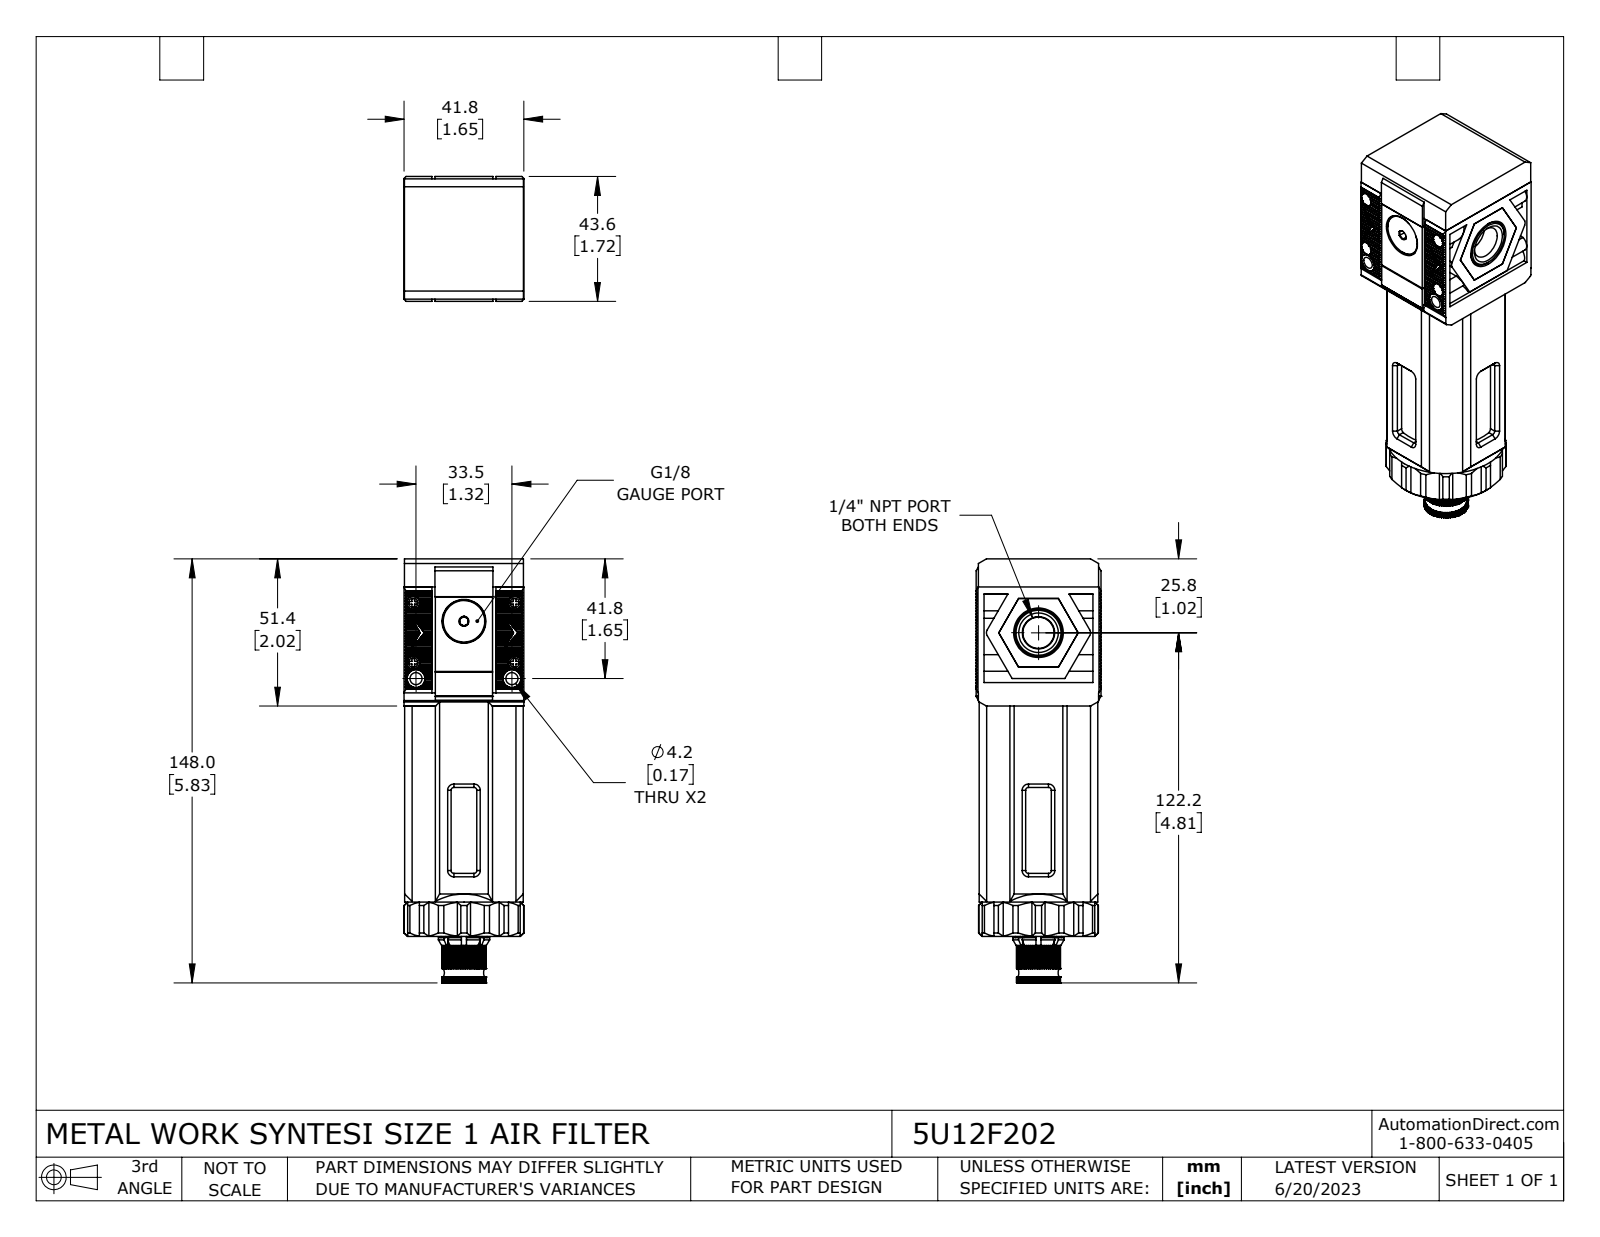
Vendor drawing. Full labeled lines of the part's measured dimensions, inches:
Part name (STEP PRODUCT): 5U12F202
STEP written by: SolidWorks 2021 (CONFIG_CONTROL_DESIGN)
Units: inches
Bodies: 14 solids, 1872 faces (1424 planar, 286 cylindrical, 162 other)
Overall size (bounding box): 5.827 × 1.717 × 1.646
Volume: 7.983 in³ · Surface area: 101.3 in²
Round holes (diameter × count): ⌀0.083 ×4, ⌀0.118 ×4, ⌀0.185 ×4, ⌀0.165 ×2, ⌀0.126 ×1, ⌀0.276 ×1, ⌀0.337 ×1, ⌀0.343 ×1, ⌀0.602 ×1, ⌀1.181 ×1, ⌀1.339 ×1, ⌀1.394 ×1
Round bosses / shafts (diameter × count): ⌀0.181 ×4, ⌀0.102 ×4, ⌀0.244 ×2, ⌀1.63 ×1, ⌀1.402 ×1, ⌀0.984 ×1, ⌀0.898 ×1, ⌀0.717 ×1
Partial cylindrical surfaces — rounded edges, fillets, slot ends (radius × count): R0.039 ×8, R0.024 ×4, R0.122 ×4, R0.008 ×2, R0.079 ×2, R0.276 ×1, R0.28 ×1, R0.354 ×1
Main face-to-face distances: 1.638, 1.63, 0.043, 1.673, 0.386, 1.331, 1.642, 0.307, 1.575, 0.067
Hole centre spacings: 0.222, 0.742, 0.823, 0.9, 1.027, 1.042, 1.374, 1.394
